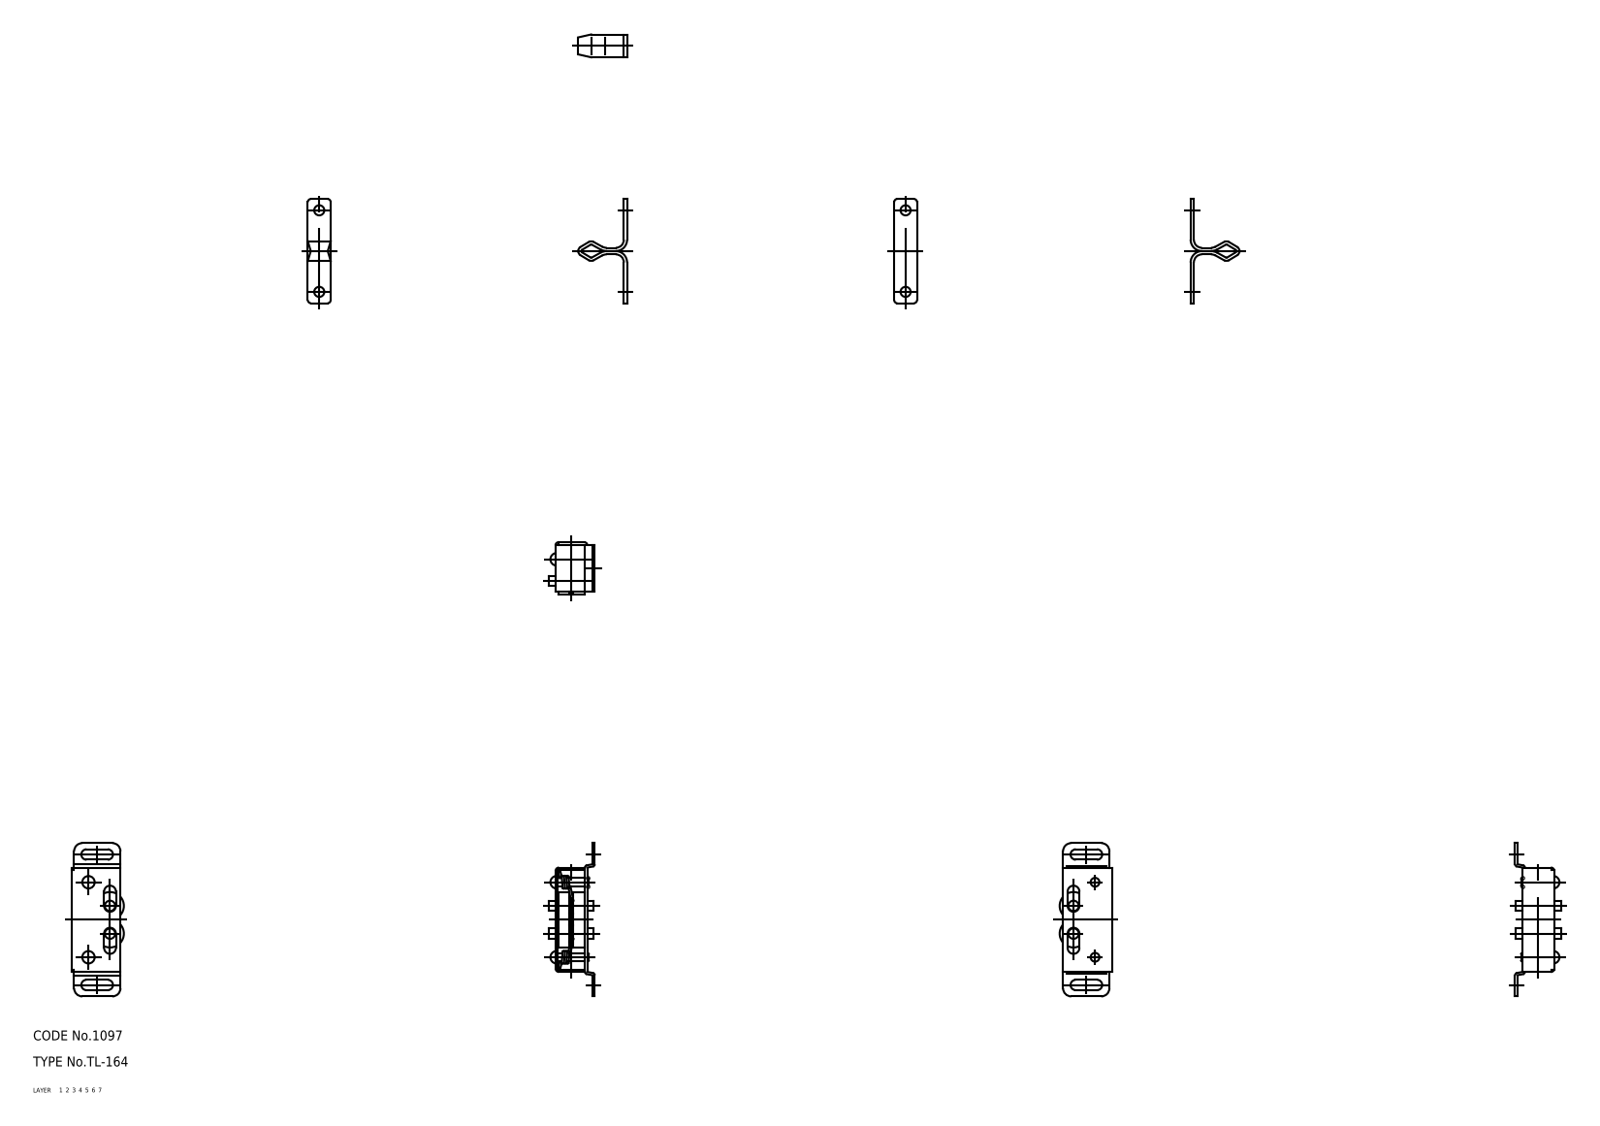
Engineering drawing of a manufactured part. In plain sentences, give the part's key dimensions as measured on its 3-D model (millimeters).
The part is named "cap; roller; shaft; spring_mr (+4 more)". Its 3-D file was written by "CADfix (AUTOMOTIVE_DESIGN)". It is 12 solids with 201 faces: 0 planar, 0 cylindrical and 201 other. Overall it measures 47 by 44 by 14 millimeters. Its volume is 2 543 cubic millimeters and its surface area 5 620 square millimeters.
